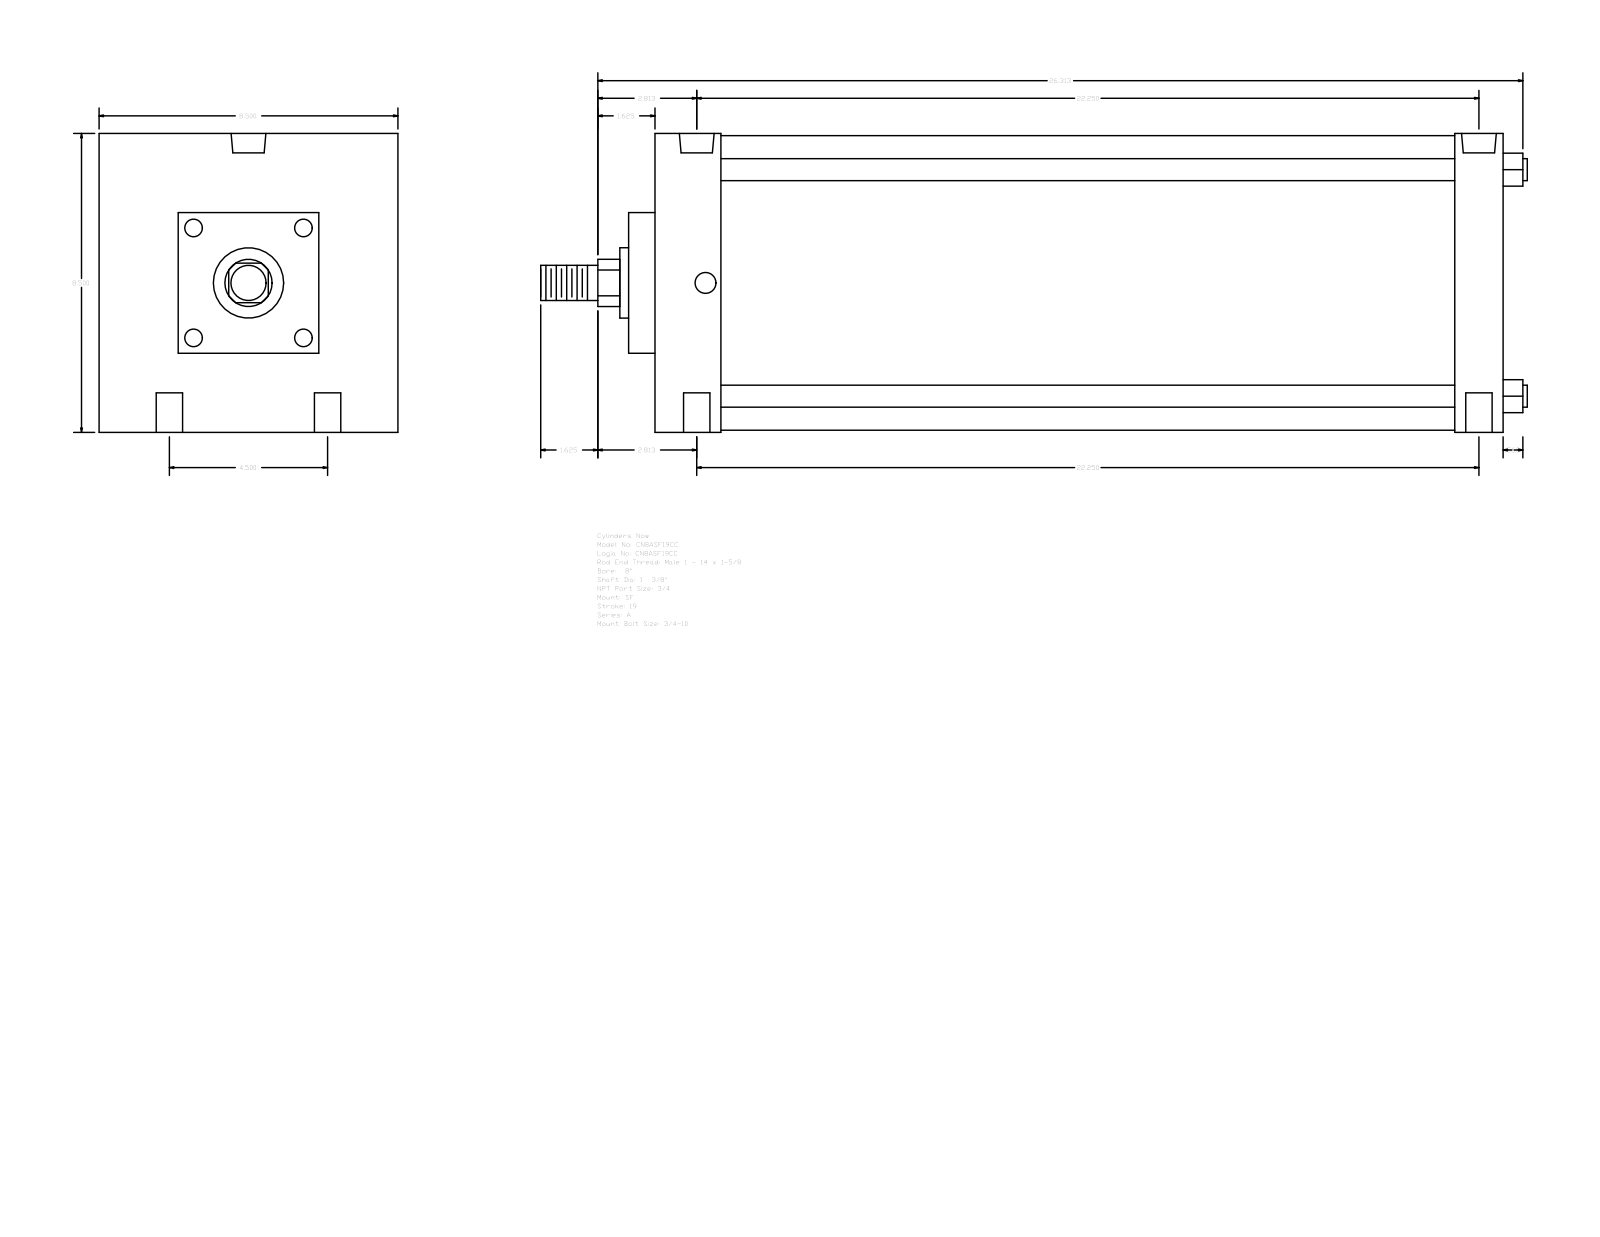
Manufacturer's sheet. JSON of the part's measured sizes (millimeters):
{"part_name": "A_SF__0800_1.375", "step_written_by": "GSSL Pune (CONFIG_CONTROL_DESIGN)", "units": "millimeters", "bodies": {"solids": 0, "faces": 93, "planar": 67, "cylindrical": 26, "other": 0}, "overall_size": [712.79, 215.9, 215.9], "round_holes": [[19.05, 4], [15.08, 2], [25.12, 2]], "round_bosses_or_shafts": [[15.88, 4], [212.72, 1], [50.8, 1], [34.92, 1], [25.4, 1]], "partial_cylinders_radius": [[17.06, 1]], "face_to_face_distances": [612.78, 215.9, 47.63, 577.85, 530.22, 565.15, 34.93, 19.04, 66.67, 596.89], "hole_center_spacings": [57.15, 568.03, 565.15, 114.3, 576.59, 552.45]}
